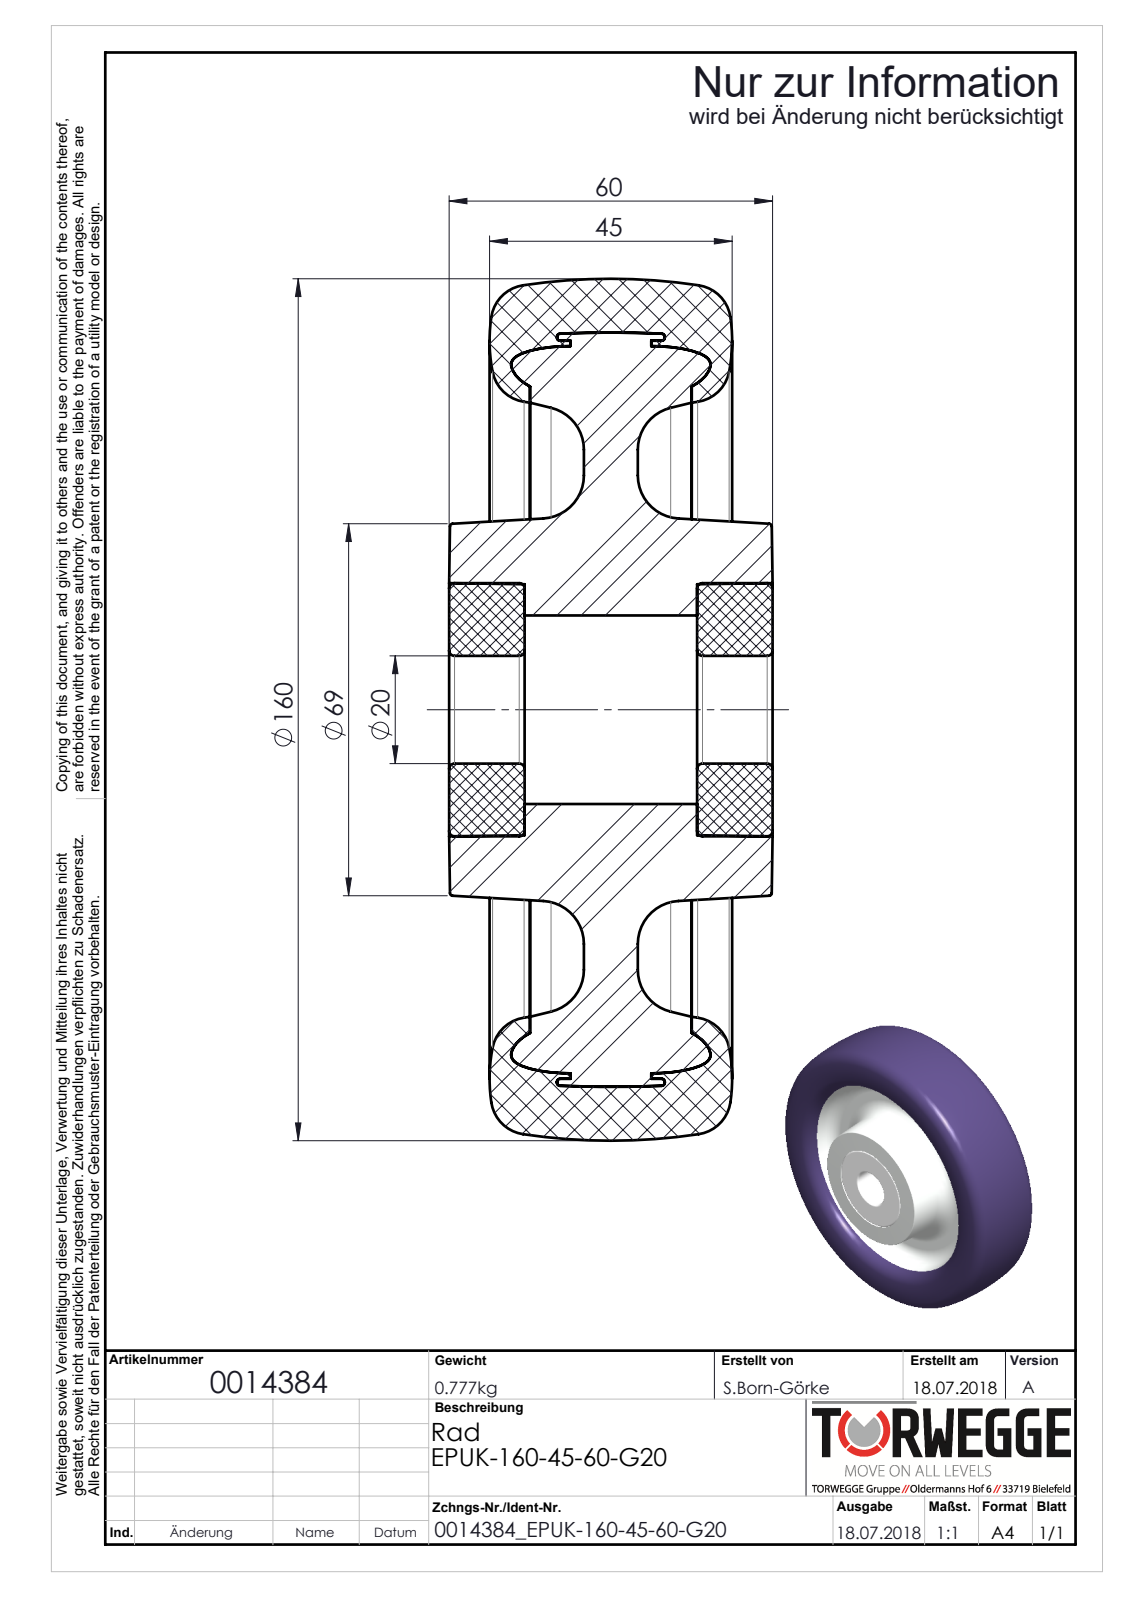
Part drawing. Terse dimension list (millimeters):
name: 0014384_EPUK-160-45-60-G20
written by: SolidWorks 2016 (AUTOMOTIVE_DESIGN)
unit: mm
bodies: 0 solids, 70 faces (6 planar, 6 cylindrical, 58 other)
size: 160 × 160 × 60
holes: 1× ⌀20, 1× ⌀35
face distances: 10, 25, 35, 15, 45, 20, 60, 30
